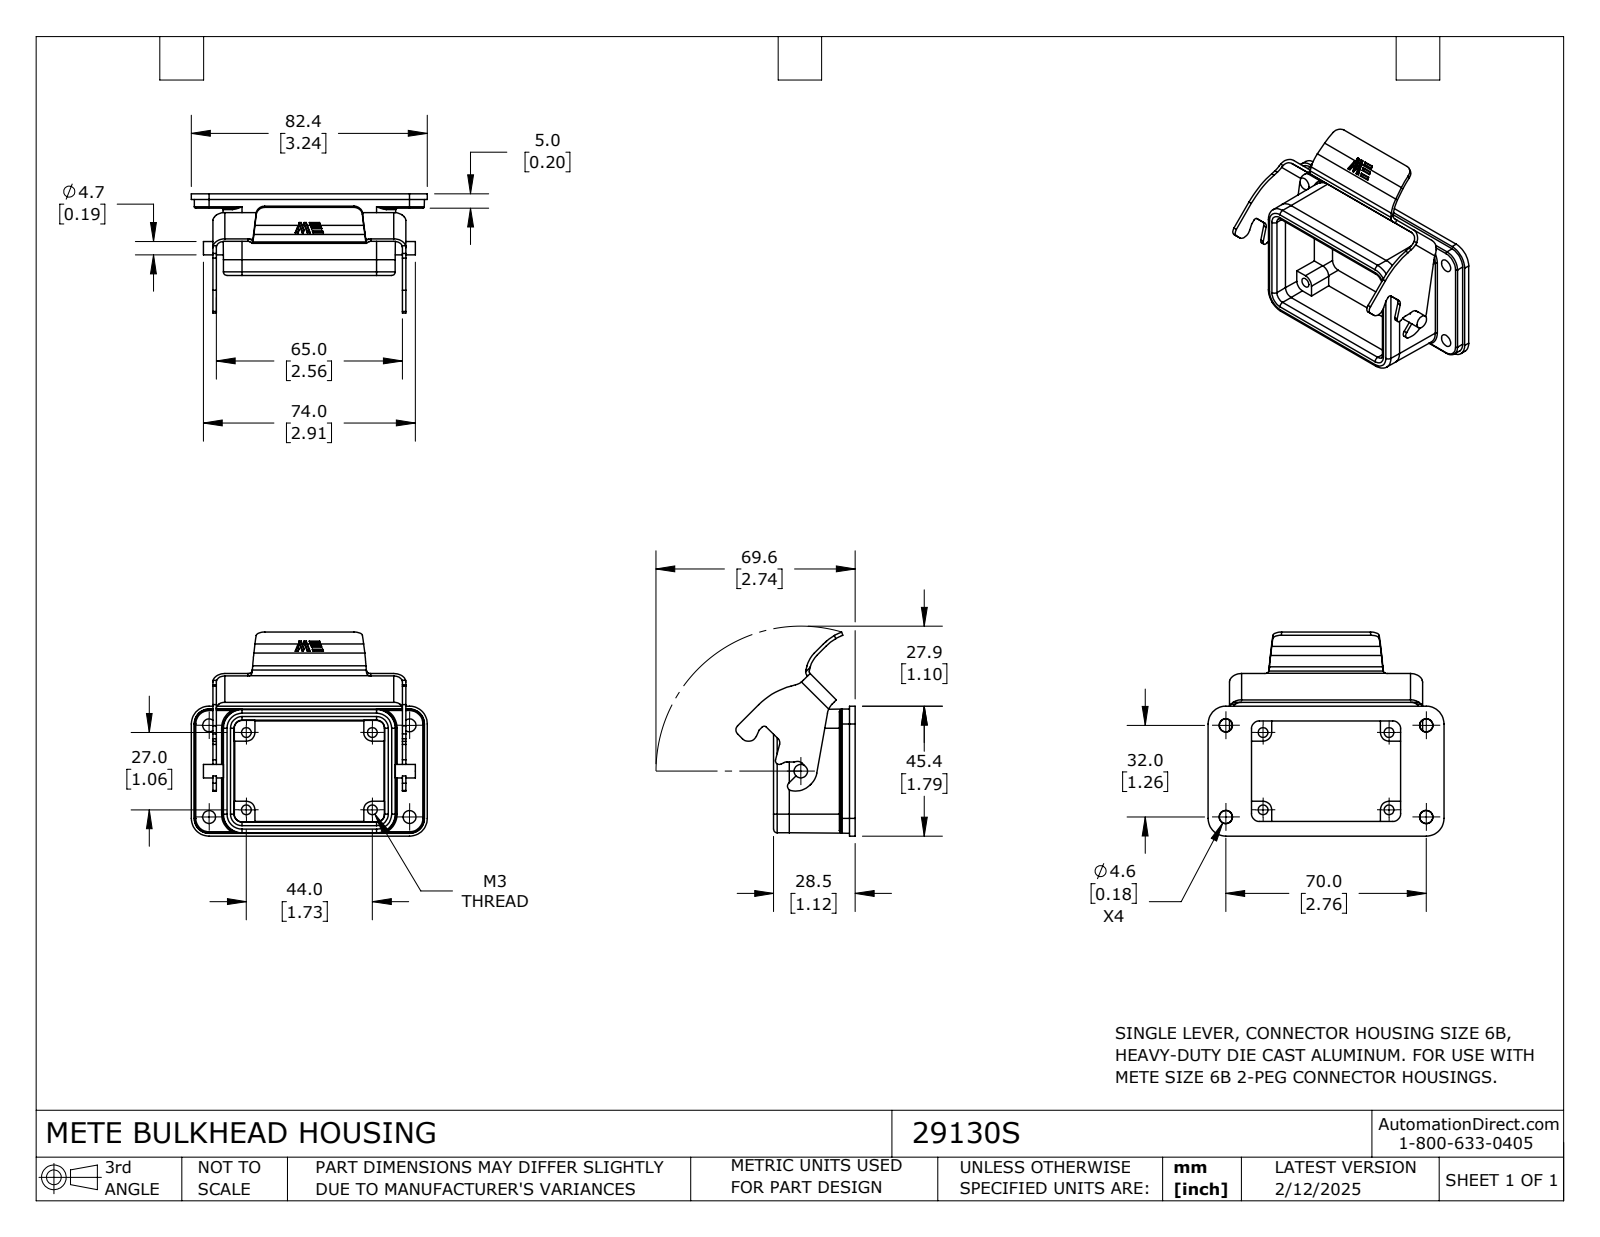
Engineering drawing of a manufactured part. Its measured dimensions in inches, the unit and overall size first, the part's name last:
Units: inches
Overall size (bounding box): 3.243 × 2.805 × 1.64
Round holes (diameter × count): ⌀0.134 ×4, ⌀0.183 ×4
Round bosses / shafts (diameter × count): ⌀0.185 ×1
Partial cylindrical surfaces — rounded edges, fillets, slot ends (radius × count): R0.008 ×16, R0.118 ×9, R0.049 ×8, R0.02 ×6, R0.109 ×4, R0.11 ×4, R0.204 ×4, R0.244 ×4
Main face-to-face distances: 0.047, 2.606, 0.146, 0.197, 0.155, 2.559, 2.654, 0.301, 2.353, 0.254
Hole centre spacings: 0.521, 1.269, 2.246, 2.527, 1.063, 1.26, 1.732, 2.032
Volume: 1.823 in³ · Surface area: 33.82 in²
Bodies: 1 solid, 281 faces (105 planar, 132 cylindrical, 44 other)
Part name (STEP PRODUCT): 29130S
STEP written by: SolidWorks 2024 (CONFIG_CONTROL_DESIGN)
